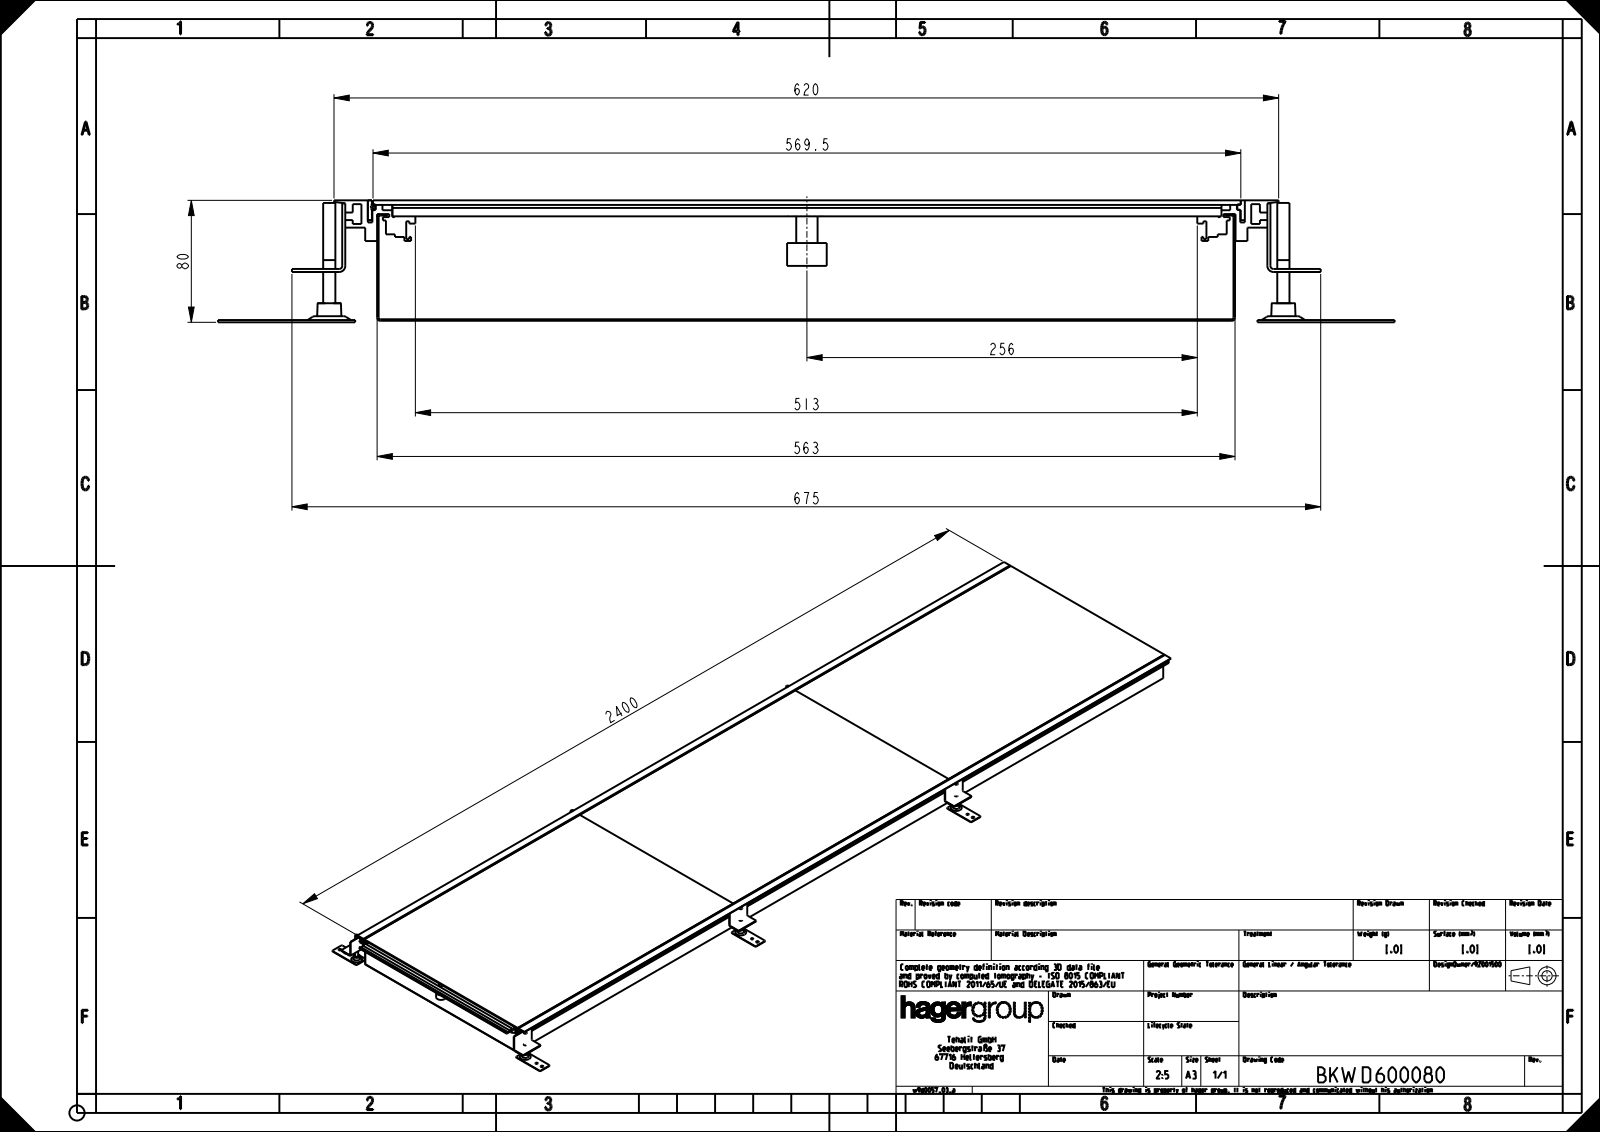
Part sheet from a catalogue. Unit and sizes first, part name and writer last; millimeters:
Units: millimetres
Overall size (bounding box): 2432.5 × 772.13 × 80
Round holes (diameter × count): ⌀7 ×15, ⌀8 ×9, ⌀10 ×9, ⌀6 ×6, ⌀8.5 ×6, ⌀11.5 ×6, ⌀17.5 ×6, ⌀23 ×6
Round bosses / shafts (diameter × count): ⌀26 ×9, ⌀14 ×9, ⌀11.9 ×9, ⌀20 ×6, ⌀8 ×6
Partial cylindrical surfaces — rounded edges, fillets, slot ends (radius × count): R2 ×96, R3 ×24, R0.5 ×20, R1 ×4, R4 ×2
Main face-to-face distances: 1, 3, 76, 79, 75, 78, 562, 7.5, 6.5, 68.5
Hole centre spacings: 800, 1600, 800.25, 801.1, 802.4, 1042.3, 1055.24, 1083.09
Volume: 10 360 000 mm³ · Surface area: 8 686 000 mm²
Bodies: 61 solids, 1036 faces (606 planar, 358 cylindrical, 72 other)
Part name (STEP PRODUCT): U05644KUN; U05650KUN; U05647KUN; U05826KUN (+8 more)
STEP written by: CREO PARAMETRIC BY PTC INC, 2020281 (AUTOMOTIVE_DESIGN)
